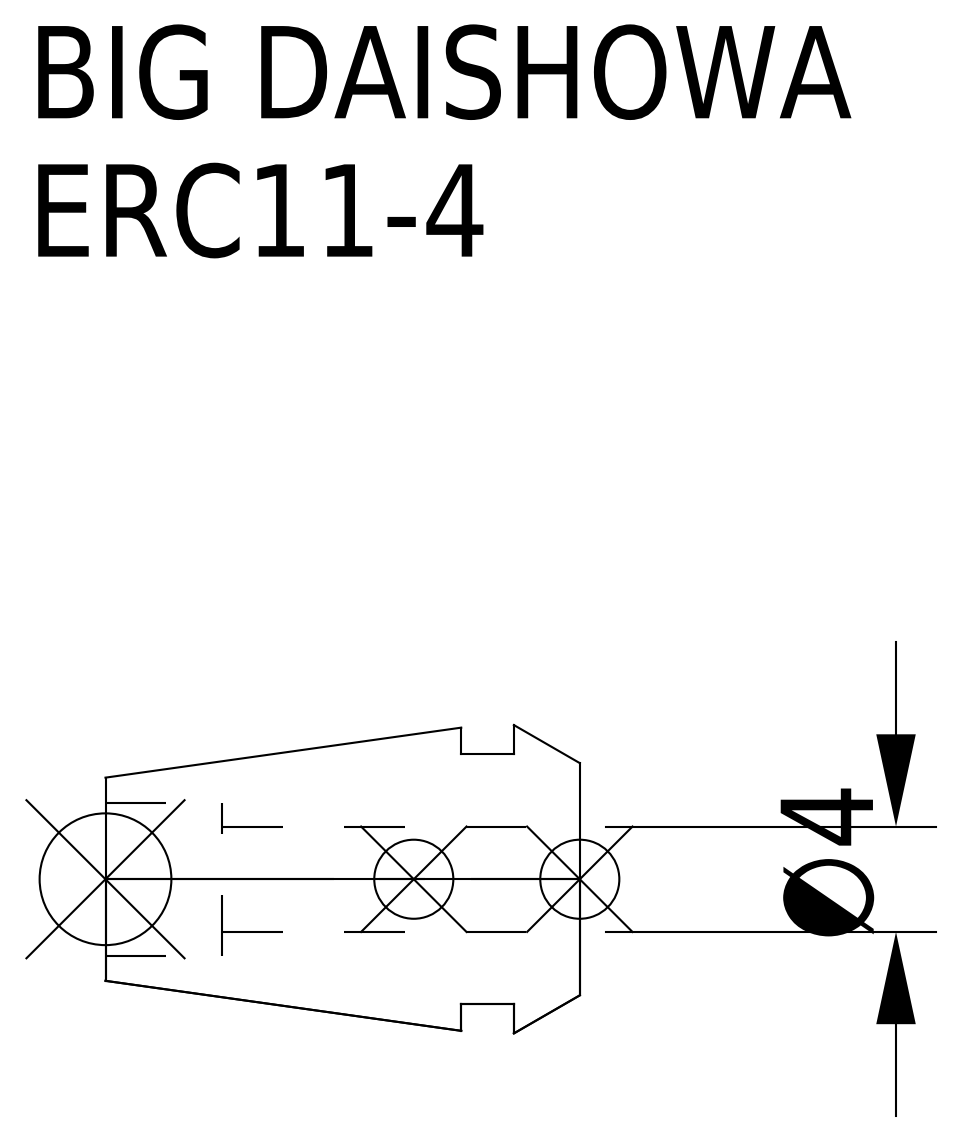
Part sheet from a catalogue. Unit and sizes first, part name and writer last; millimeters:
Units: millimetres
Overall size (bounding box): 18 × 11.7 × 11.7
Round holes (diameter × count): ⌀4 ×1, ⌀5.8 ×1
Round bosses / shafts (diameter × count): ⌀9.5 ×1
Main face-to-face distances: 2.5, 4.5, 2, 18, 15.5, 13.5, 13.58, 11.08, 9.08, 4.42
Volume: 1 054 mm³ · Surface area: 968 mm²
Bodies: 1 solid, 15 faces (5 planar, 6 cylindrical, 4 other)
Part name (STEP PRODUCT): ERC11-4
STEP written by: CREO PARAMETRIC BY PTC INC, 2016380 (AUTOMOTIVE_DESIGN)
